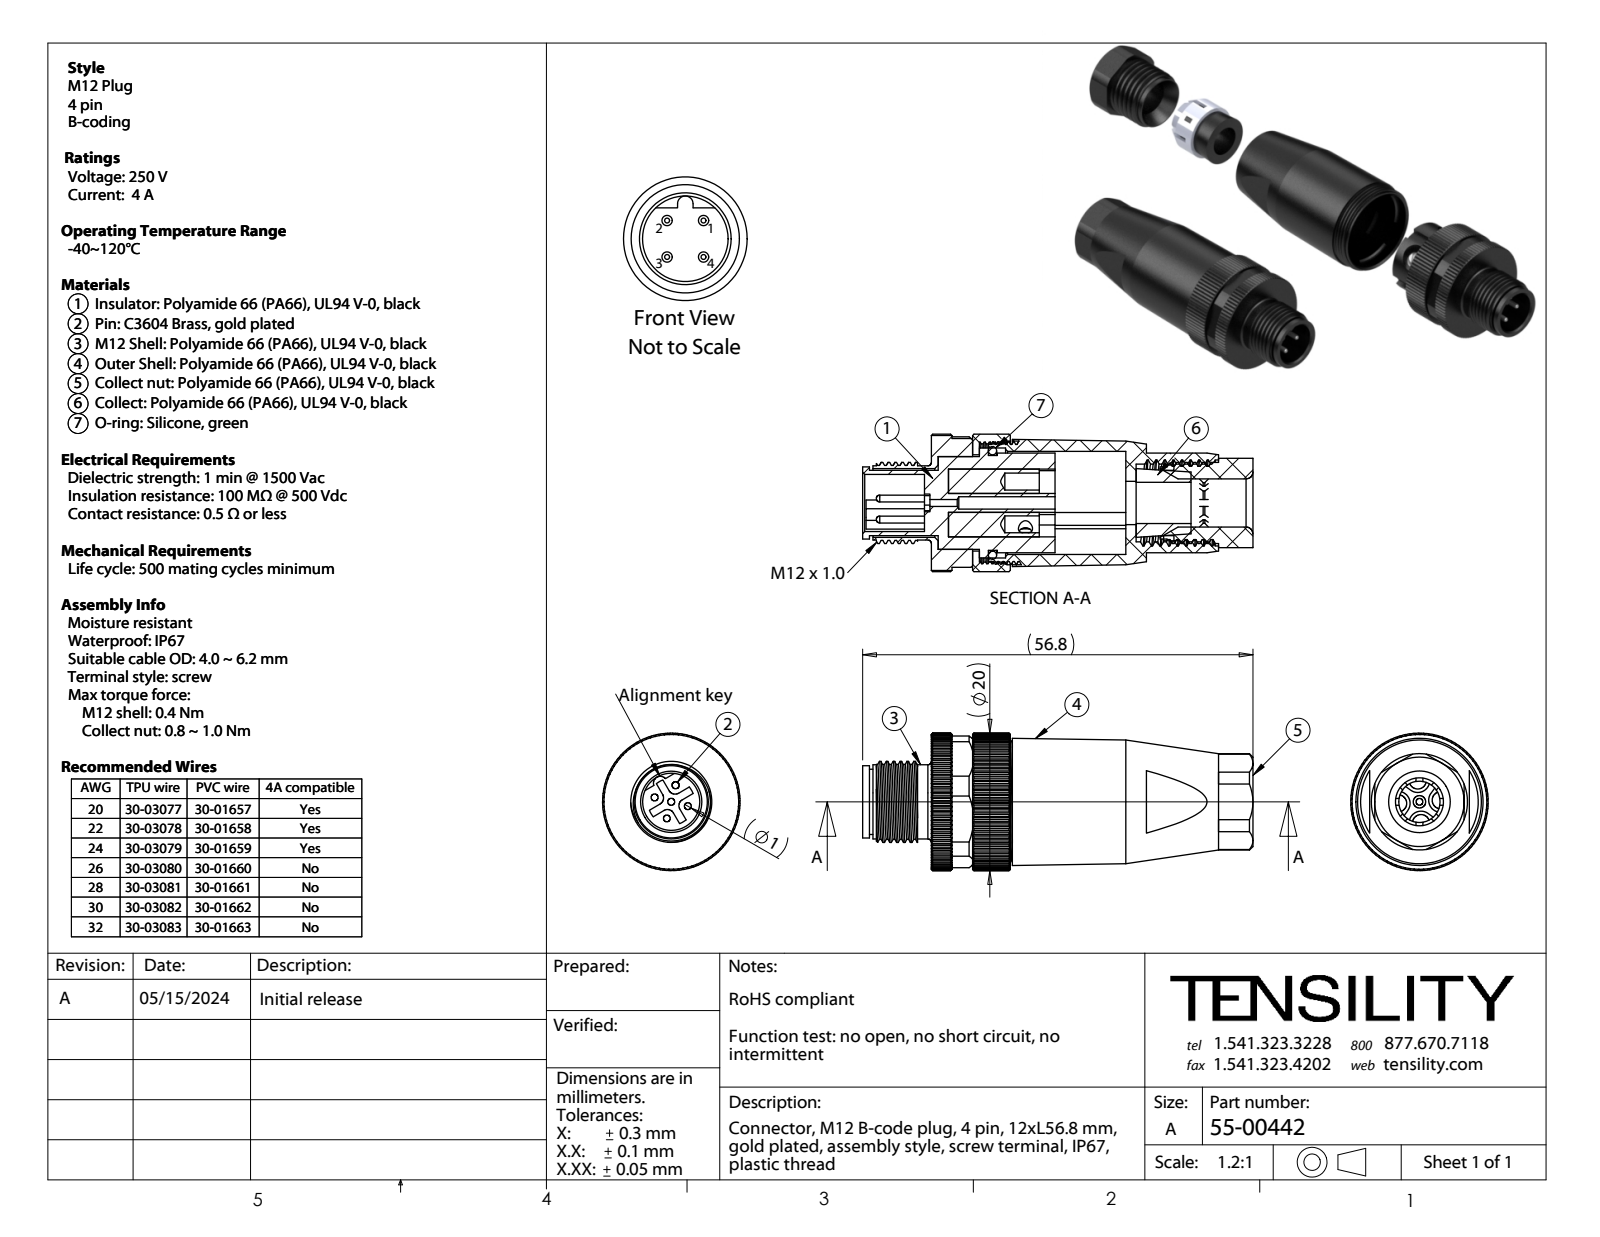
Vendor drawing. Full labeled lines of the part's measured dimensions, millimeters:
Part name (STEP PRODUCT): 55-00442-05; 55-00442_revA; 55-00442-06; 55-00442-10 (+6 more)
STEP written by: SolidWorks 2021 (CONFIG_CONTROL_DESIGN)
Units: millimetres
Bodies: 12 solids, 1449 faces (530 planar, 448 cylindrical, 471 other)
Overall size (bounding box): 56.8 × 20 × 20
Volume: 8 486 mm³ · Surface area: 13 254 mm²
Round holes (diameter × count): ⌀2.5 ×8, ⌀1 ×5, ⌀2.05 ×4, ⌀5 ×4, ⌀1.8 ×1, ⌀6 ×1, ⌀6.3 ×1, ⌀7 ×1, ⌀8.3 ×1, ⌀9.5 ×1, ⌀10 ×1, ⌀11.3 ×1
Round bosses / shafts (diameter × count): ⌀20 ×1, ⌀17.8 ×1, ⌀17.03 ×1, ⌀17 ×1, ⌀14.5 ×1, ⌀14 ×1, ⌀13.8 ×1, ⌀11.8 ×1
Partial cylindrical surfaces — rounded edges, fillets, slot ends (radius × count): R1 ×5, R1.75 ×4, R3.4 ×1, R5.3 ×1, R6.45 ×1, R6.5 ×1, R9.65 ×1
Main face-to-face distances: 1, 6, 1.5, 27.3, 28.8, 7, 13.86, 17, 5, 23.8
Hole centre spacings: 5.14, 5.13, 0.8, 2.5, 3.12, 3.54, 3.62, 4.34
